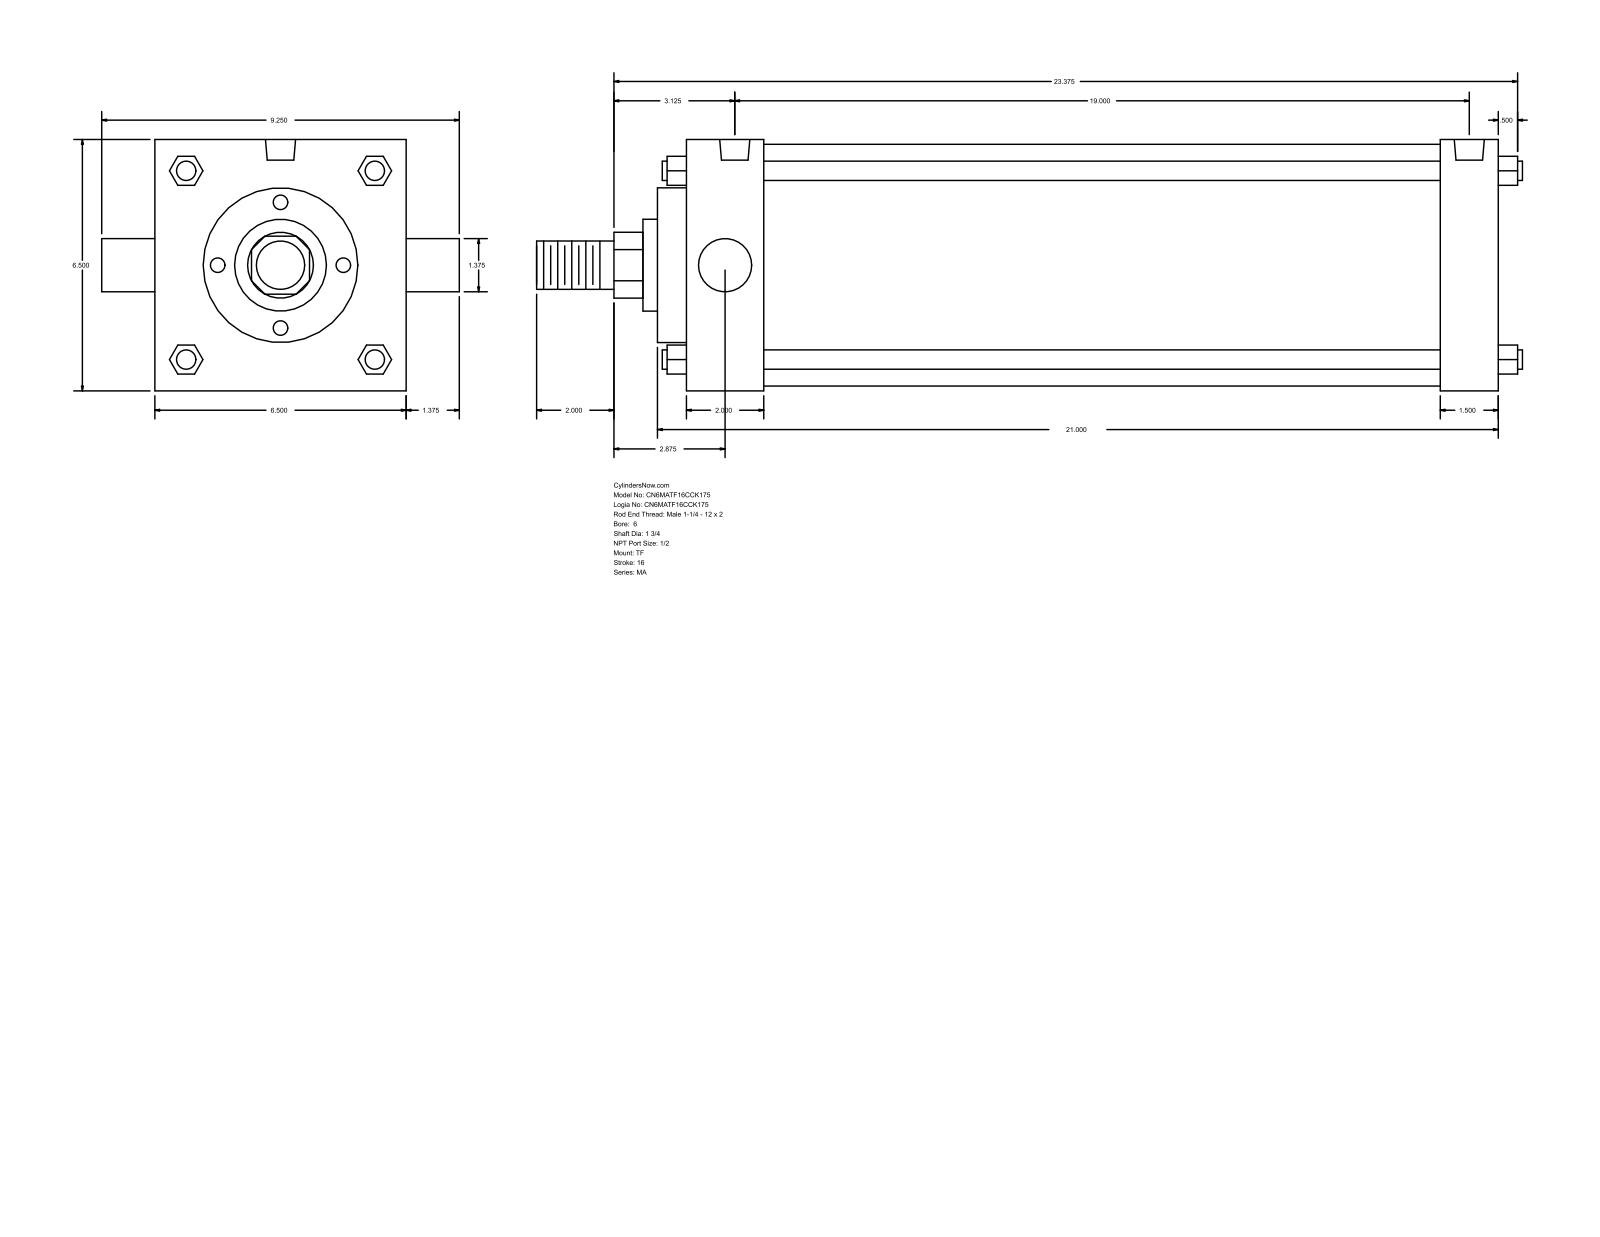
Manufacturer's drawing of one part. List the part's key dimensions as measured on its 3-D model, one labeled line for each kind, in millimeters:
Part name (STEP PRODUCT): MA_TF__0600_1.75
STEP written by: GSSL Pune (CONFIG_CONTROL_DESIGN)
Units: millimetres
Bodies: 0 solids, 122 faces (93 planar, 29 cylindrical, 0 other)
Overall size (bounding box): 647.7 × 234.95 × 165.1
Round holes (diameter × count): ⌀17.46 ×3, ⌀19.77 ×2
Round bosses / shafts (diameter × count): ⌀12.7 ×4, ⌀158.75 ×1, ⌀101.6 ×1, ⌀60.33 ×1, ⌀44.45 ×1, ⌀34.92 ×1, ⌀31.75 ×1
Partial cylindrical surfaces — rounded edges, fillets, slot ends (radius × count): R21.63 ×1
Main face-to-face distances: 165.1, 533.4, 19.05, 38.1, 50.8, 482.6, 495.3, 444.5, 69.85, 514.35
Hole centre spacings: 482.6
